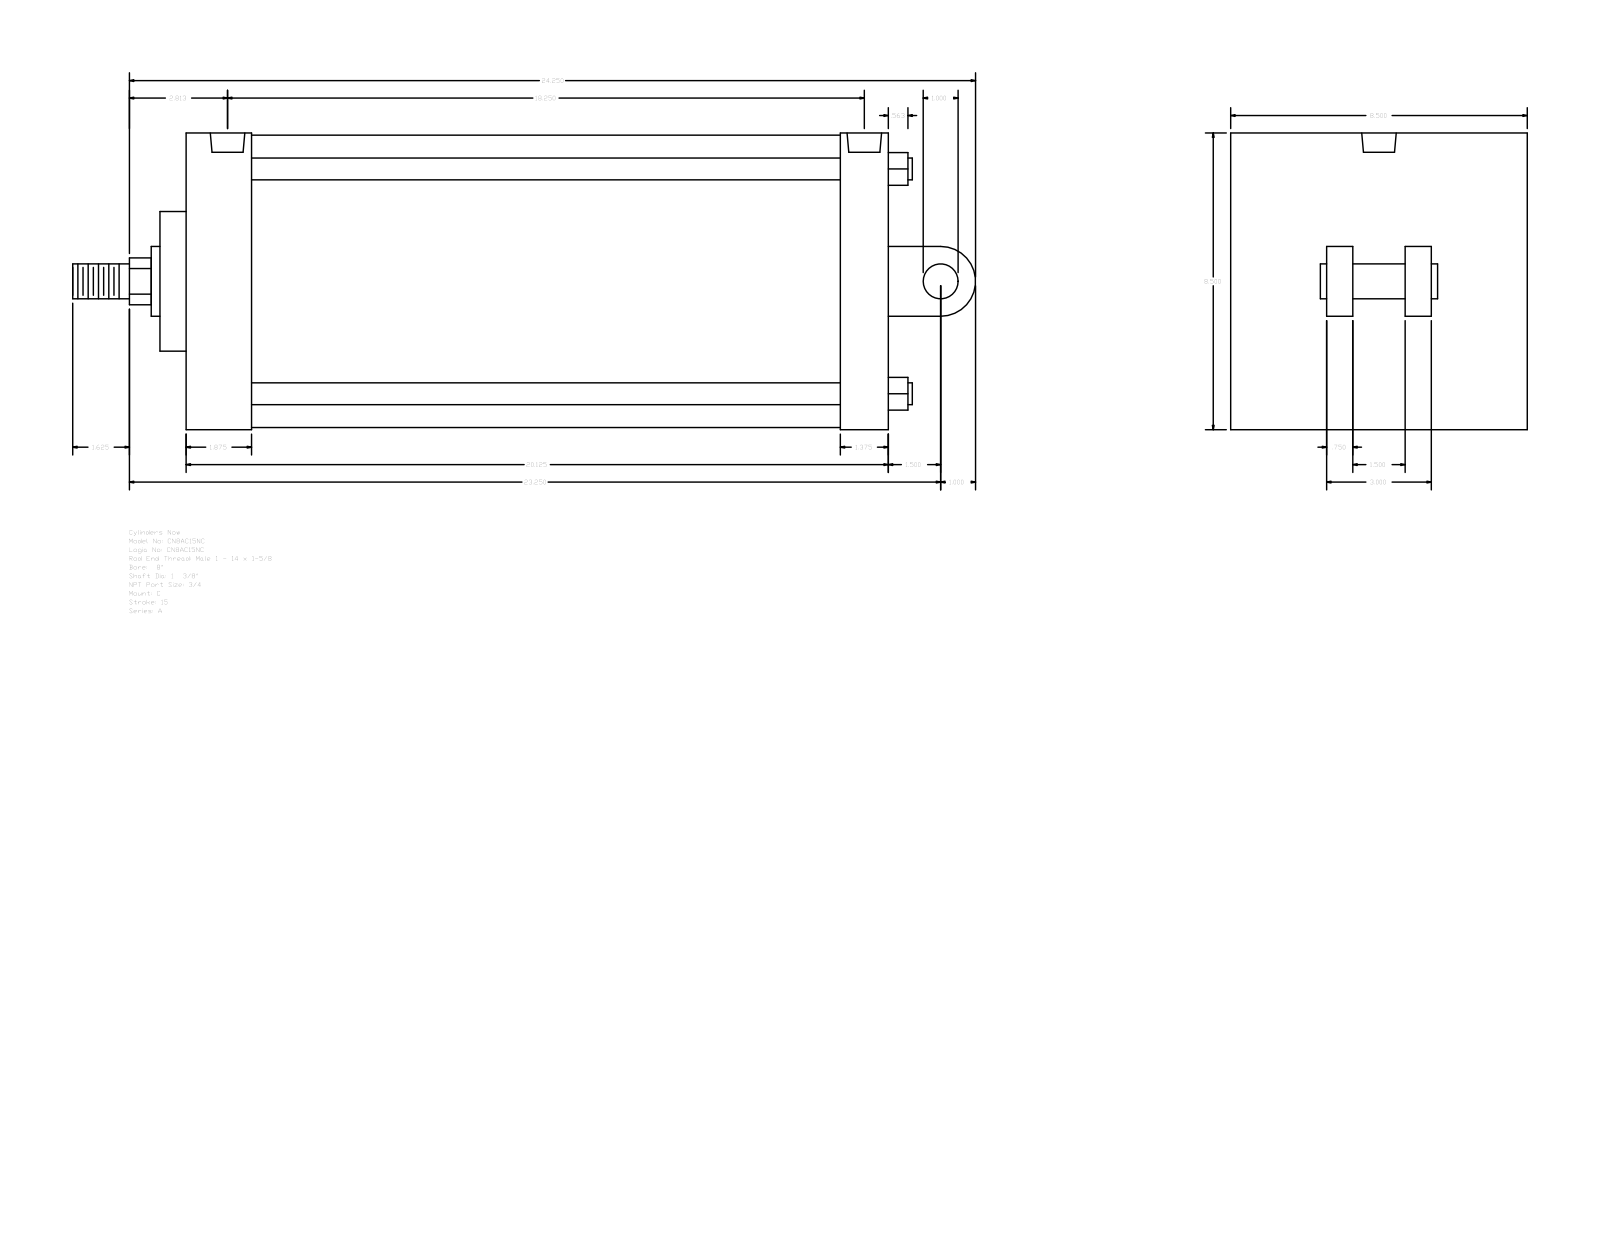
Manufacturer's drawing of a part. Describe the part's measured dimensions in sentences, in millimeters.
The part is named "A_C__0800_1.375". Its 3-D file was written by "GSSL Pune (CONFIG_CONTROL_DESIGN)". It is 0 solids with 104 faces: 75 planar, 29 cylindrical and 0 other. Overall it measures 657.23 by 215.9 by 215.9 millimeters. Round holes: 4 of diameter 15.08, 2 of diameter 25.12. Round bosses or shafts: 4 of diameter 15.88, 2 of diameter 25.4, 1 of diameter 212.72, 1 of diameter 50.8, 1 of diameter 34.92. Partial cylindrical surfaces (rounded edges, fillets, slot ends): 1 of radius 17.06, 1 of radius 25.4. The main face-to-face distances are 511.18, 215.9, 57.15, 47.63, 463.55, 476.25, 428.62, 34.93, 88.9, 69.85. The hole center spacings are 6.35, 450.85, 457.2, 463.55.
